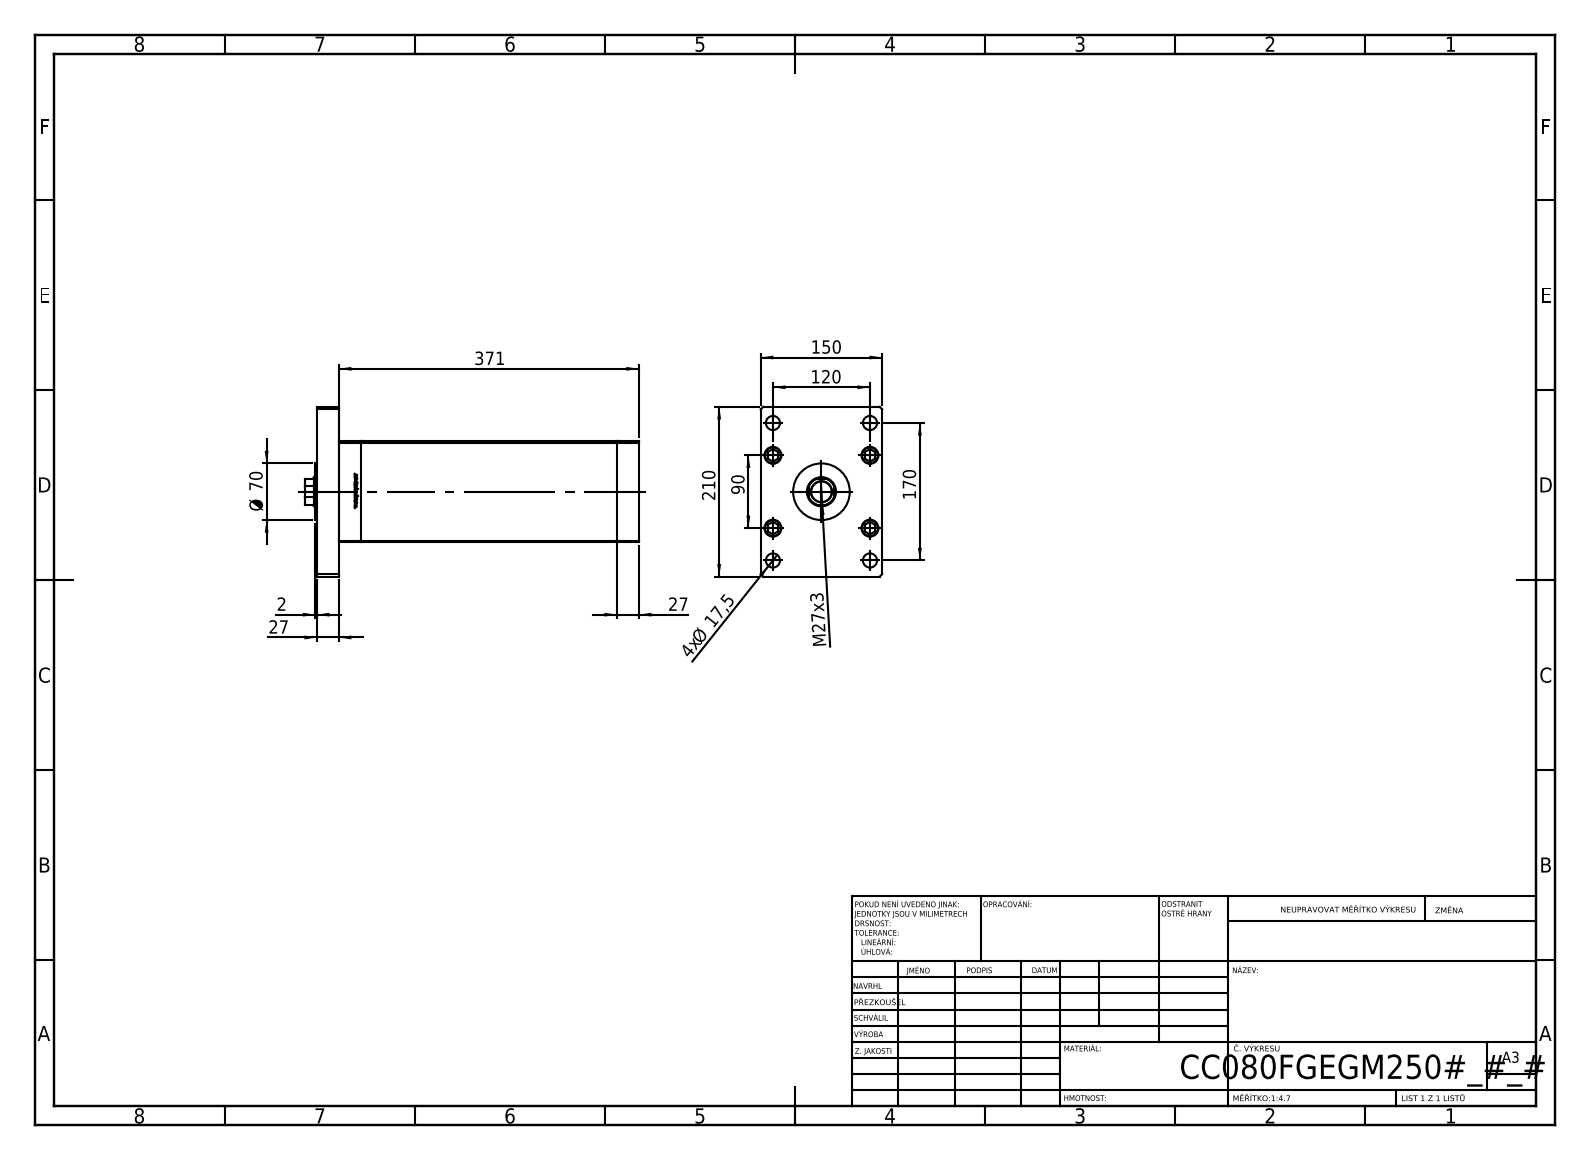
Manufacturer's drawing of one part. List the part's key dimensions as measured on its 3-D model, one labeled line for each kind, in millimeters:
Part name (STEP PRODUCT): V220C_VC_F; V220C_F; V220C BACK_F; ALLEN BOLT (+2 more)
STEP written by: SolidWorks 2019 (CONFIG_CONTROL_DESIGN)
Units: millimetres
Bodies: 19 solids, 1310 faces (517 planar, 187 cylindrical, 606 other)
Overall size (bounding box): 413 × 210 × 150
Volume: 6 544 000 mm³ · Surface area: 612 190 mm²
Round holes (diameter × count): ⌀17.5 ×9, ⌀22 ×5, ⌀16 ×4, ⌀21 ×4, ⌀2 ×2, ⌀13.16 ×2, ⌀25.5 ×1, ⌀36 ×1, ⌀37.5 ×1
Round bosses / shafts (diameter × count): ⌀8 ×9, ⌀21 ×5, ⌀80 ×1, ⌀70 ×1
Partial cylindrical surfaces — rounded edges, fillets, slot ends (radius × count): R0.93 ×2, R17.5 ×1
Main face-to-face distances: 27, 150, 125, 344, 371, 317, 54, 398, 33.5, 6.5
Hole centre spacings: 51, 40, 75, 104.04, 120, 126.49, 130, 176.92
